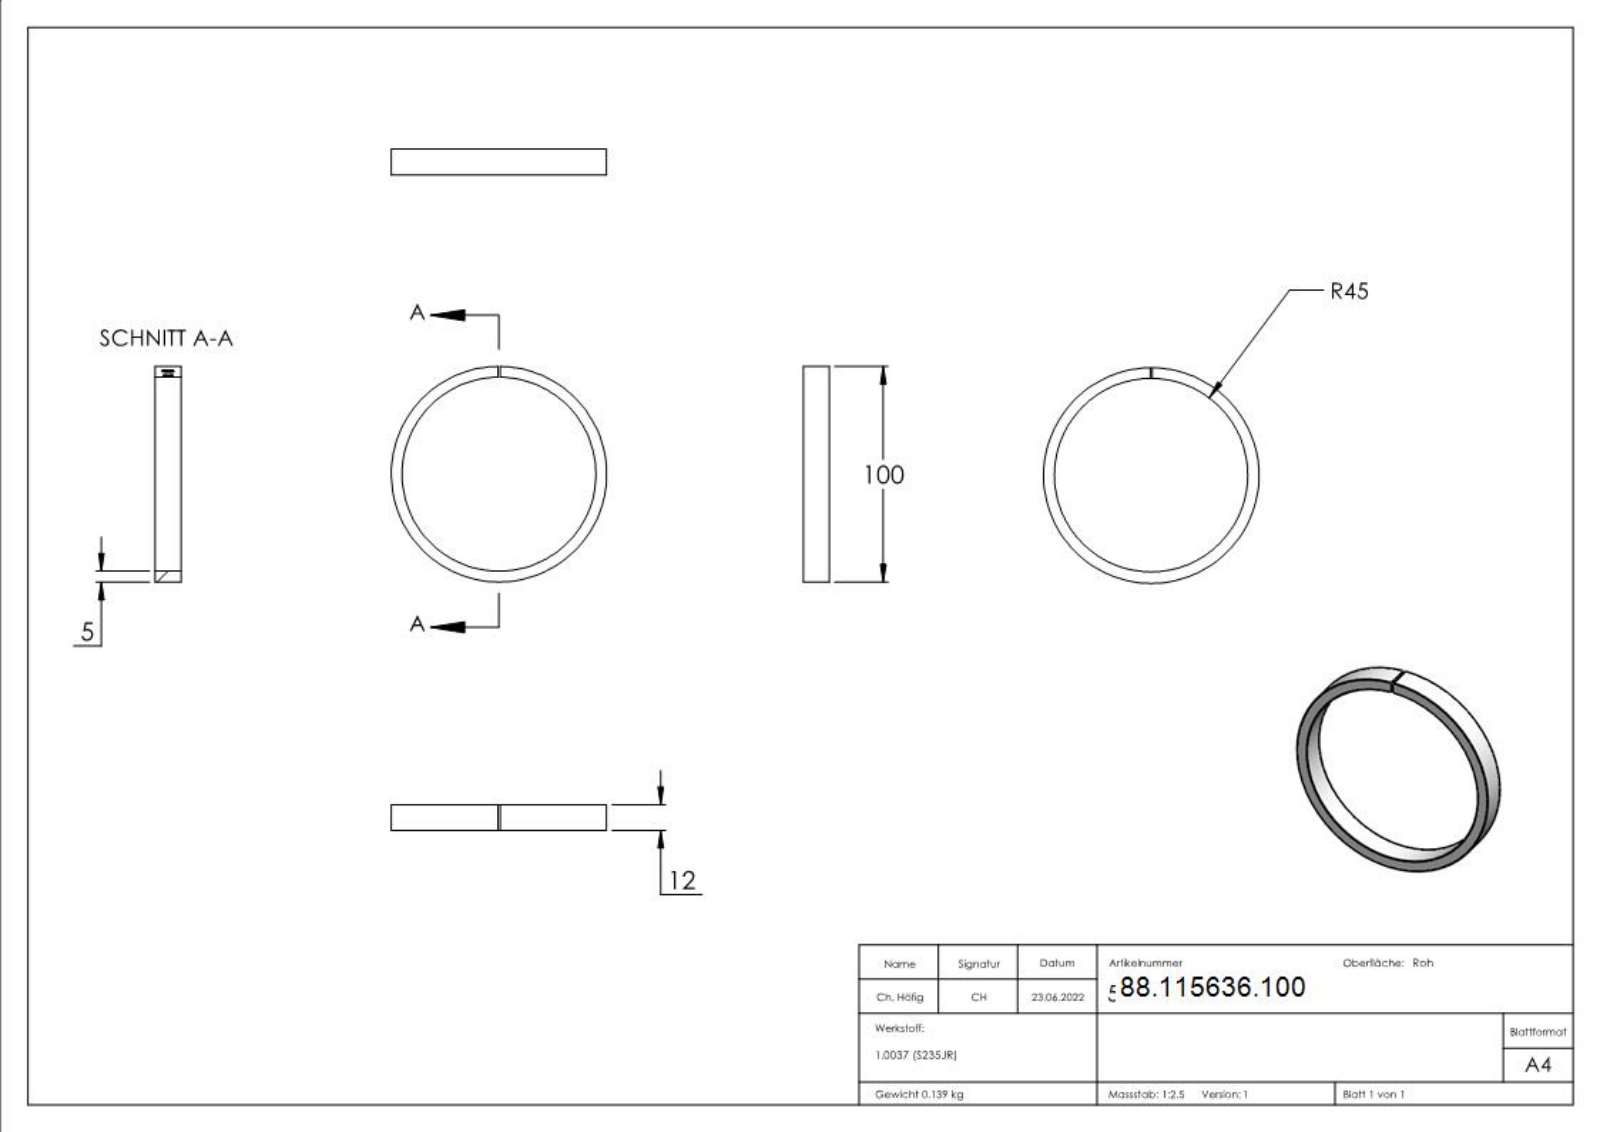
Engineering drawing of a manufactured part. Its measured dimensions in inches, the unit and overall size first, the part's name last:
Units: inches
Overall size (bounding box): 3.937 × 3.937 × 0.472
Round holes (diameter × count): ⌀3.543 ×1
Round bosses / shafts (diameter × count): ⌀3.937 ×1
Main face-to-face distances: 0.472, 0.039, 0.043, 0.07, 0.033, 0.083, 0.096, 0.039, 0.109, 0.048
Volume: 1.089 in³ · Surface area: 15.87 in²
Bodies: 1 solid, 214 faces (106 planar, 2 cylindrical, 106 other)
Part name (STEP PRODUCT): 5636-100
STEP written by: SolidWorks 2018 (CONFIG_CONTROL_DESIGN)
